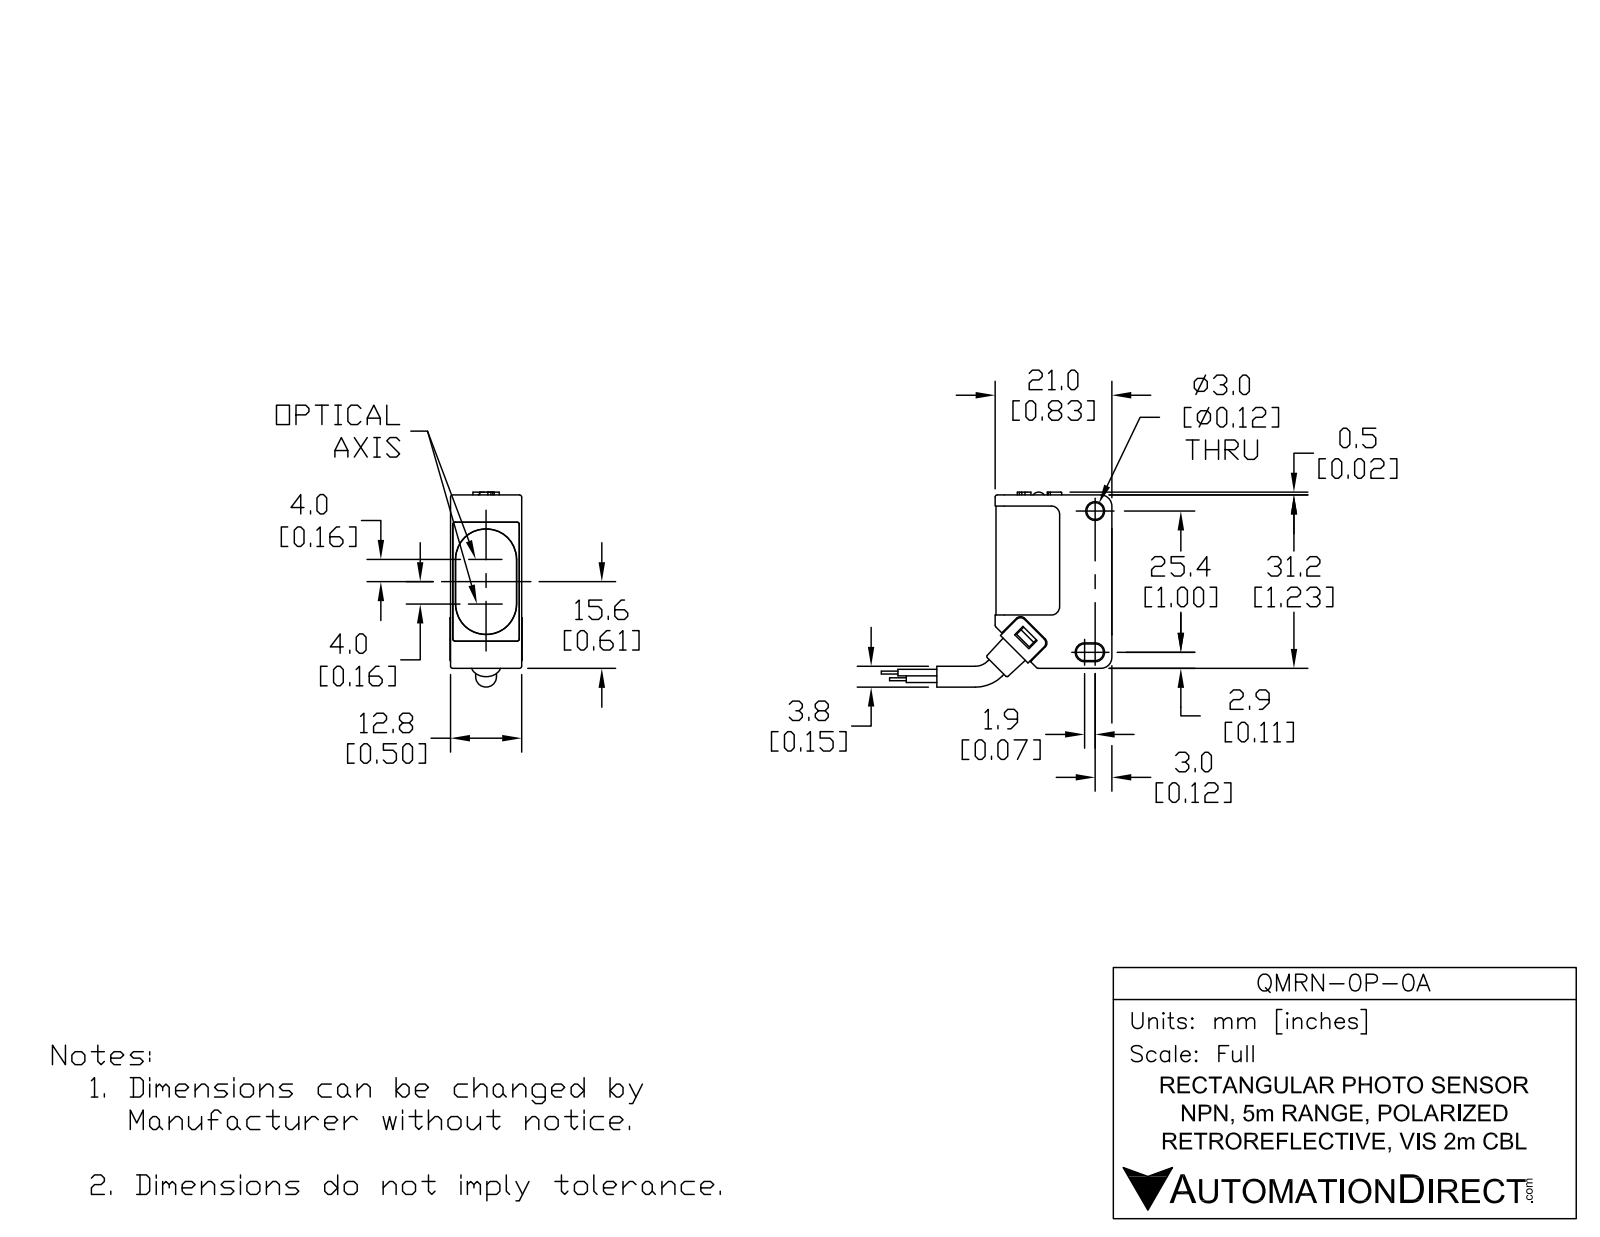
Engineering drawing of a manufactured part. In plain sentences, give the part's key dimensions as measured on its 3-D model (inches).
The part is named "QMRN-0P-0A". Its 3-D file was written by "SolidWorks 2017 (AUTOMOTIVE_DESIGN)". It is 9 solids with 258 faces: 134 planar, 100 cylindrical and 24 other. Overall it measures 3.193 by 1.032 by 0.512 inches. Its volume is 0.47 cubic inches and its surface area 8.375 square inches. Round holes: 3 of diameter 0.118, 1 of diameter 0.148, 1 of diameter 0.224, 1 of diameter 0.283. Round bosses or shafts: 2 of diameter 0.138. Partial cylindrical surfaces (rounded edges, fillets, slot ends): 13 of radius 0.016, 10 of radius 0.02, 8 of radius 0.039, 6 of radius 0.059, 4 of radius 0.024, 2 of radius 0.006, 2 of radius 0.035, 2 of radius 0.044. The main face-to-face distances are 0.02, 0.498, 0.059, 0.016, 0.504, 0.138, 0.488, 0.079, 0.482, 0.492. The hole center spacings are 0.205.
